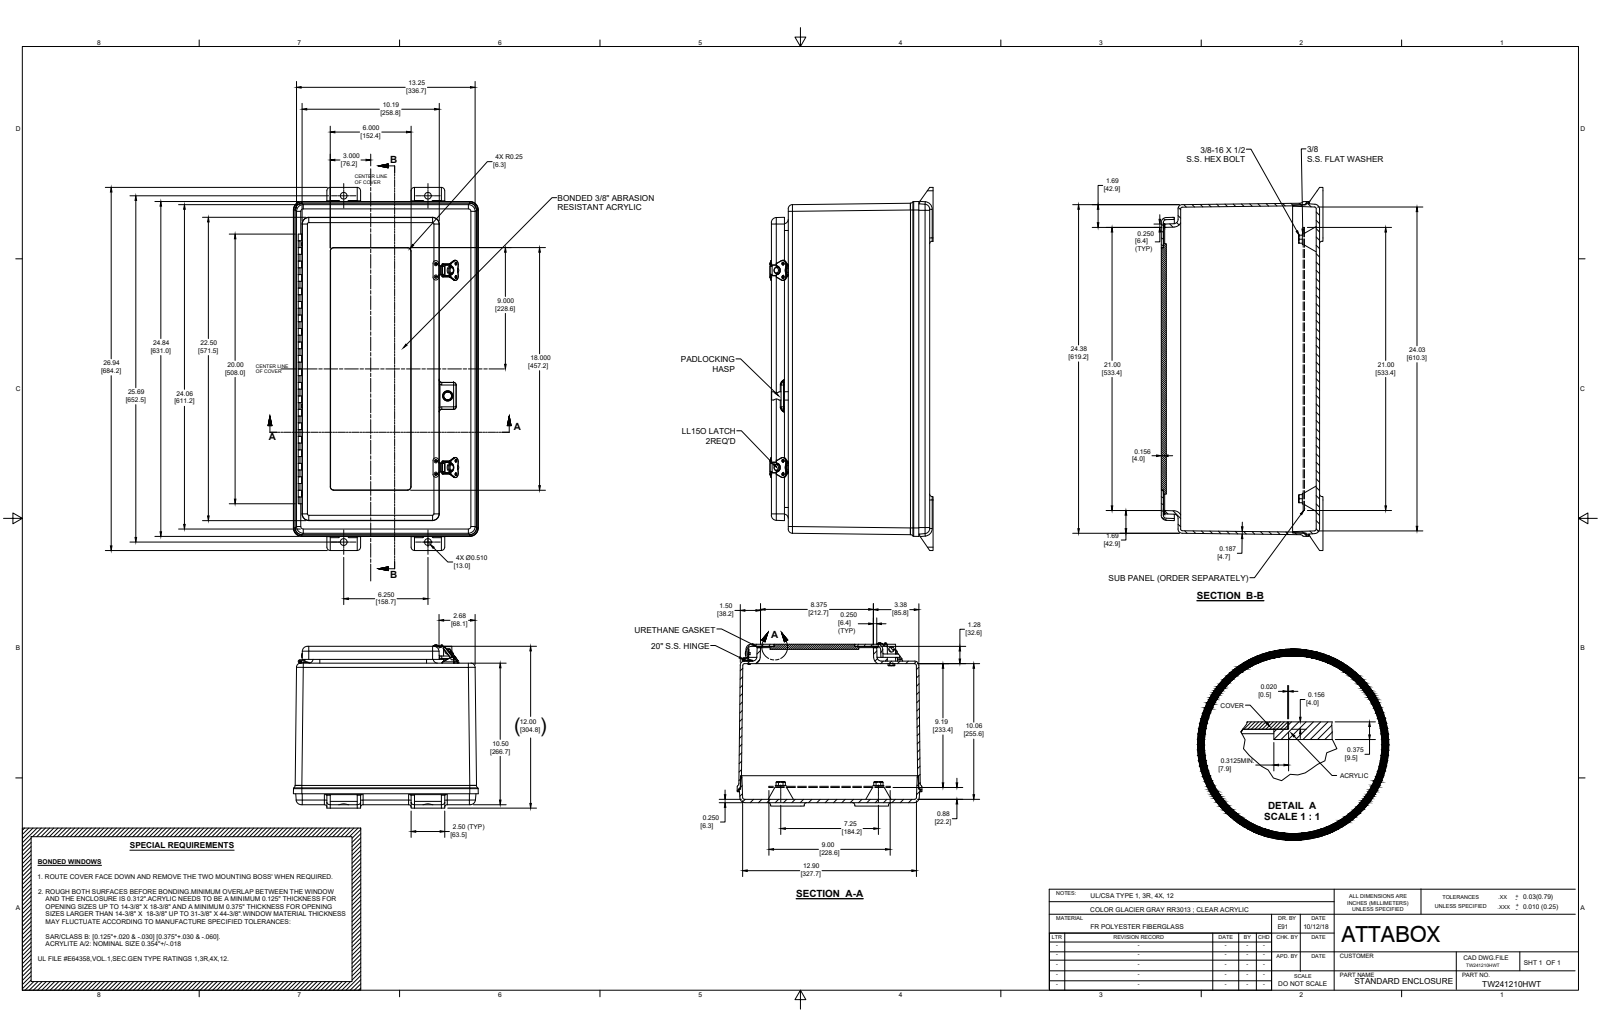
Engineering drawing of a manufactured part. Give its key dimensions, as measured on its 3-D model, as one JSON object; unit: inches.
{"part_name": "TW241210HWT", "step_written_by": "SolidWorks 2018 (AUTOMOTIVE_DESIGN)", "units": "inches", "bodies": {"solids": 41, "faces": 1211, "planar": 466, "cylindrical": 460, "other": 285}, "overall_size": [26.938, 13.719, 12.118], "volume_in3": 357.4, "surface_area_in2": 3589, "round_holes": [[0.13, 20], [0.063, 8], [0.065, 7], [0.138, 4], [0.187, 4], [0.307, 4], [0.563, 4], [0.5, 2], [0.51, 2], [0.065, 1], [0.125, 1], [0.135, 1]], "round_bosses_or_shafts": [[0.297, 8], [0.14, 8], [0.5, 2], [0.563, 1], [0.25, 1], [0.201, 1], [0.2, 1], [0.135, 1]], "partial_cylinders_radius": [[0.01, 59], [0.25, 28], [0.188, 19], [0.5, 12], [0.375, 10], [0.03, 8], [0.23, 8], [0.125, 6]], "face_to_face_distances": [0.187, 0.25, 11.722, 11.472, 11.346, 11.096, 0.375, 10.5, 0.156, 11.565], "hole_center_spacings": [14.625, 6.5, 12, 1.483, 1.483, 2.756, 3.257, 5.881]}
